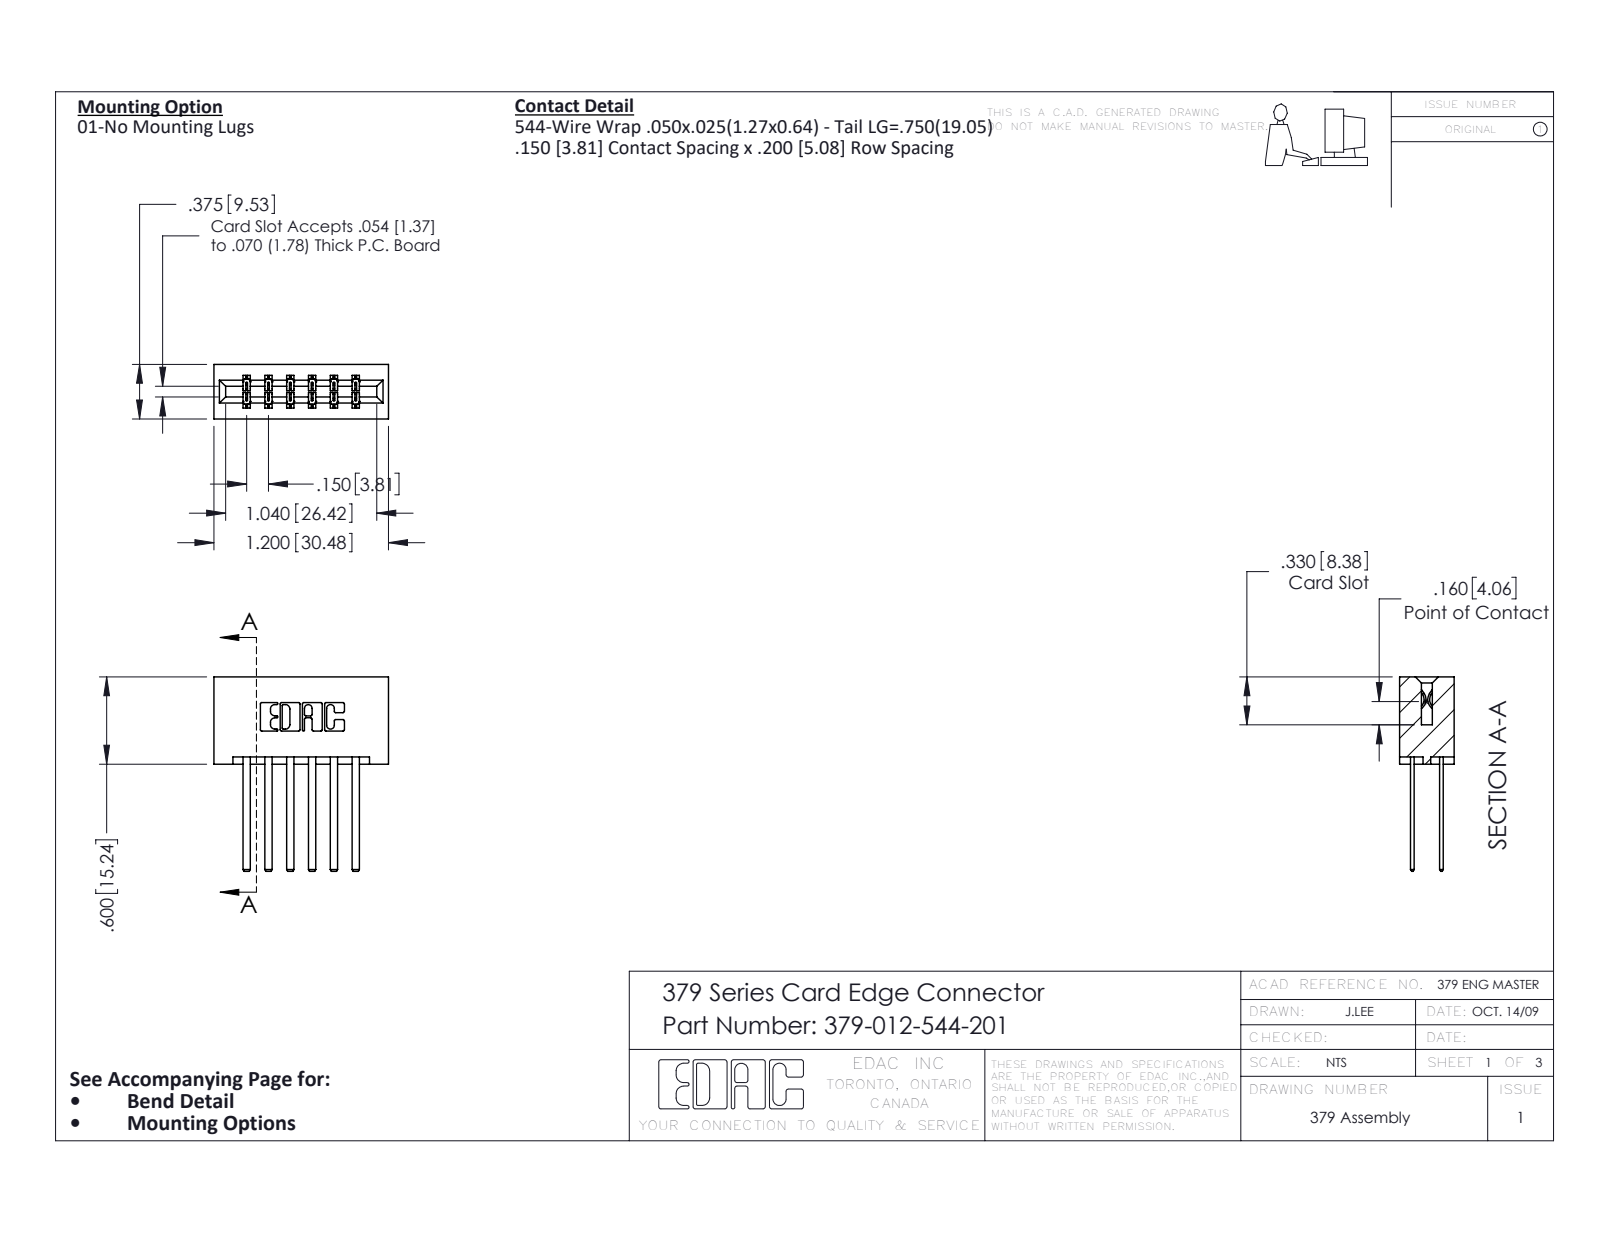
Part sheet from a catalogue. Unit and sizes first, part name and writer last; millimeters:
Units: millimetres
Overall size (bounding box): 34 × 30.5 × 9.5
Partial cylindrical surfaces — rounded edges, fillets, slot ends (radius × count): R0.3 ×22, R0.2 ×18, R0.2 ×6, R0.8 ×6, R0.7 ×3, R0.4 ×2, R0.6 ×2, R0.6 ×2
Main face-to-face distances: 7.6, 5.1, 2.5, 3.8, 1.3, 1.9, 14, 6.4, 8.9, 11.4
Volume: 3 700 mm³ · Surface area: 4 417 mm²
Bodies: 13 solids, 658 faces (450 planar, 208 cylindrical, 0 other)
Part name (STEP PRODUCT): 345-292-001_345-293-144; 379 Part_Lugless; 379-012-544-201
STEP written by: SolidWorks 2016 (CONFIG_CONTROL_DESIGN)
